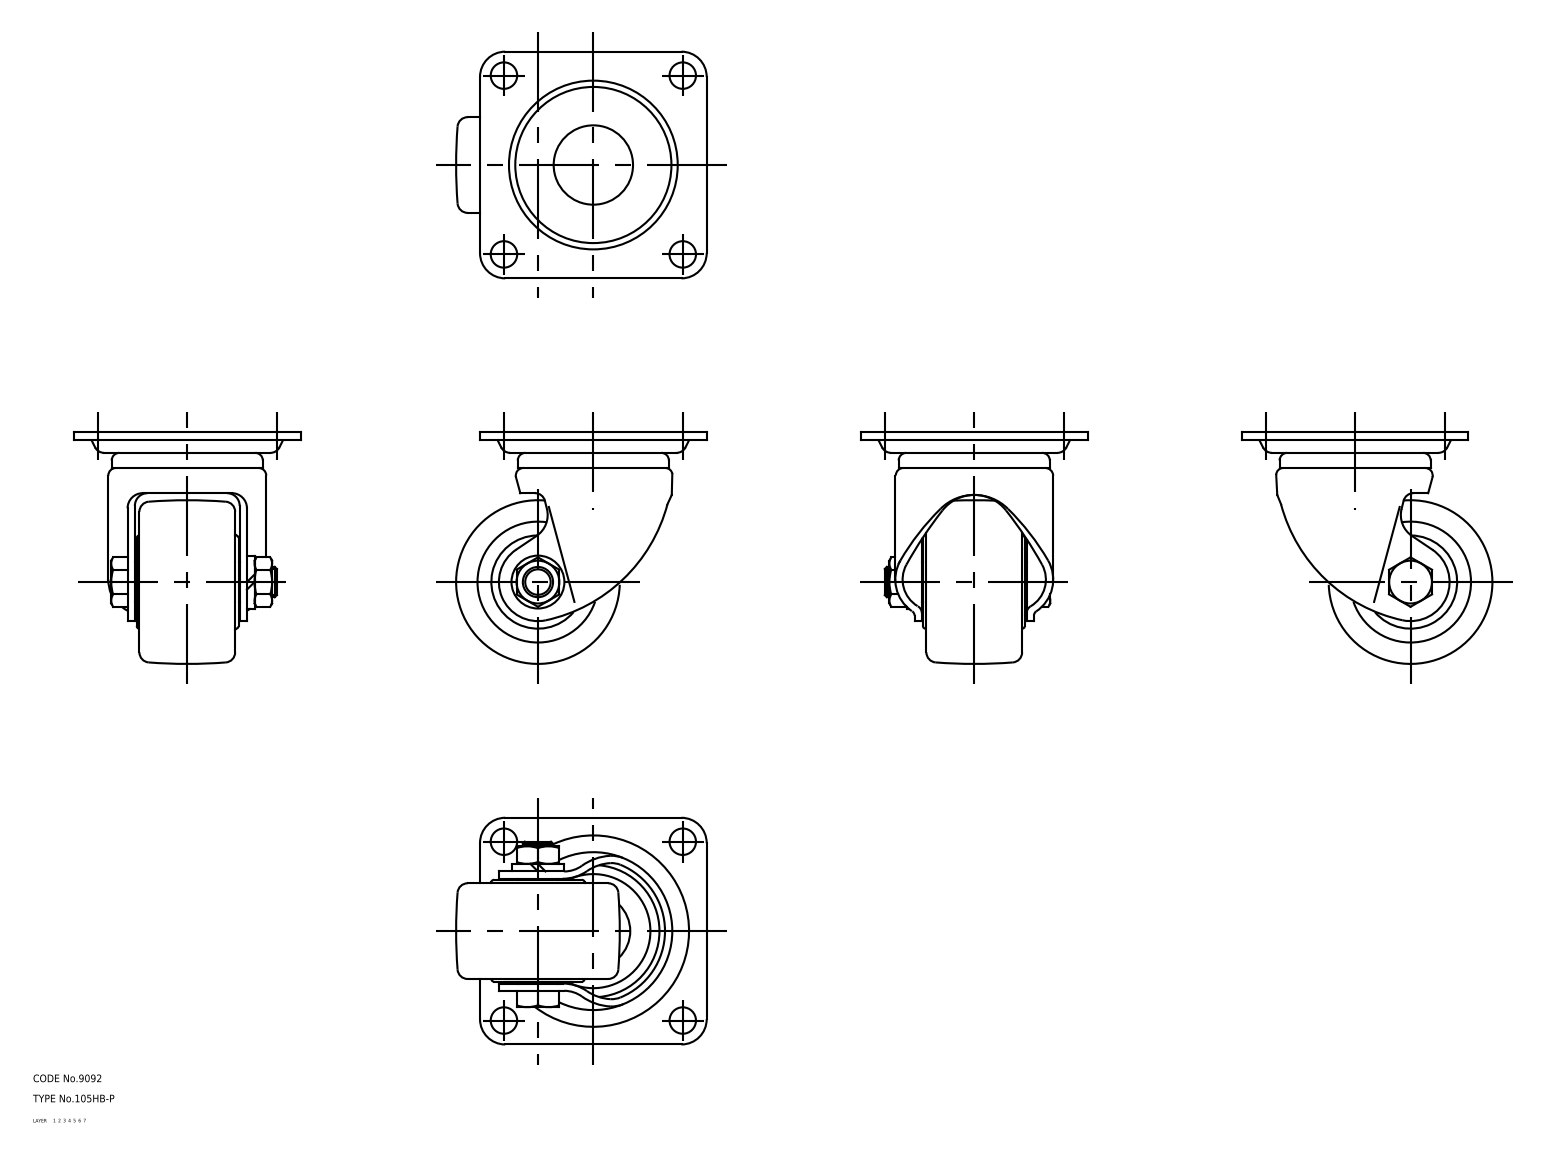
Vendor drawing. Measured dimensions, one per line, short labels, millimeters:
name: 67126126; 67126139; 67126152; 67126165 (+1 more)
written by: CADfix (AUTOMOTIVE_DESIGN)
unit: mm
bodies: 5 solids, 254 faces (0 planar, 0 cylindrical, 254 other)
size: 99.5 × 92 × 90
volume: 225 826 mm³; area: 61 732 mm²
